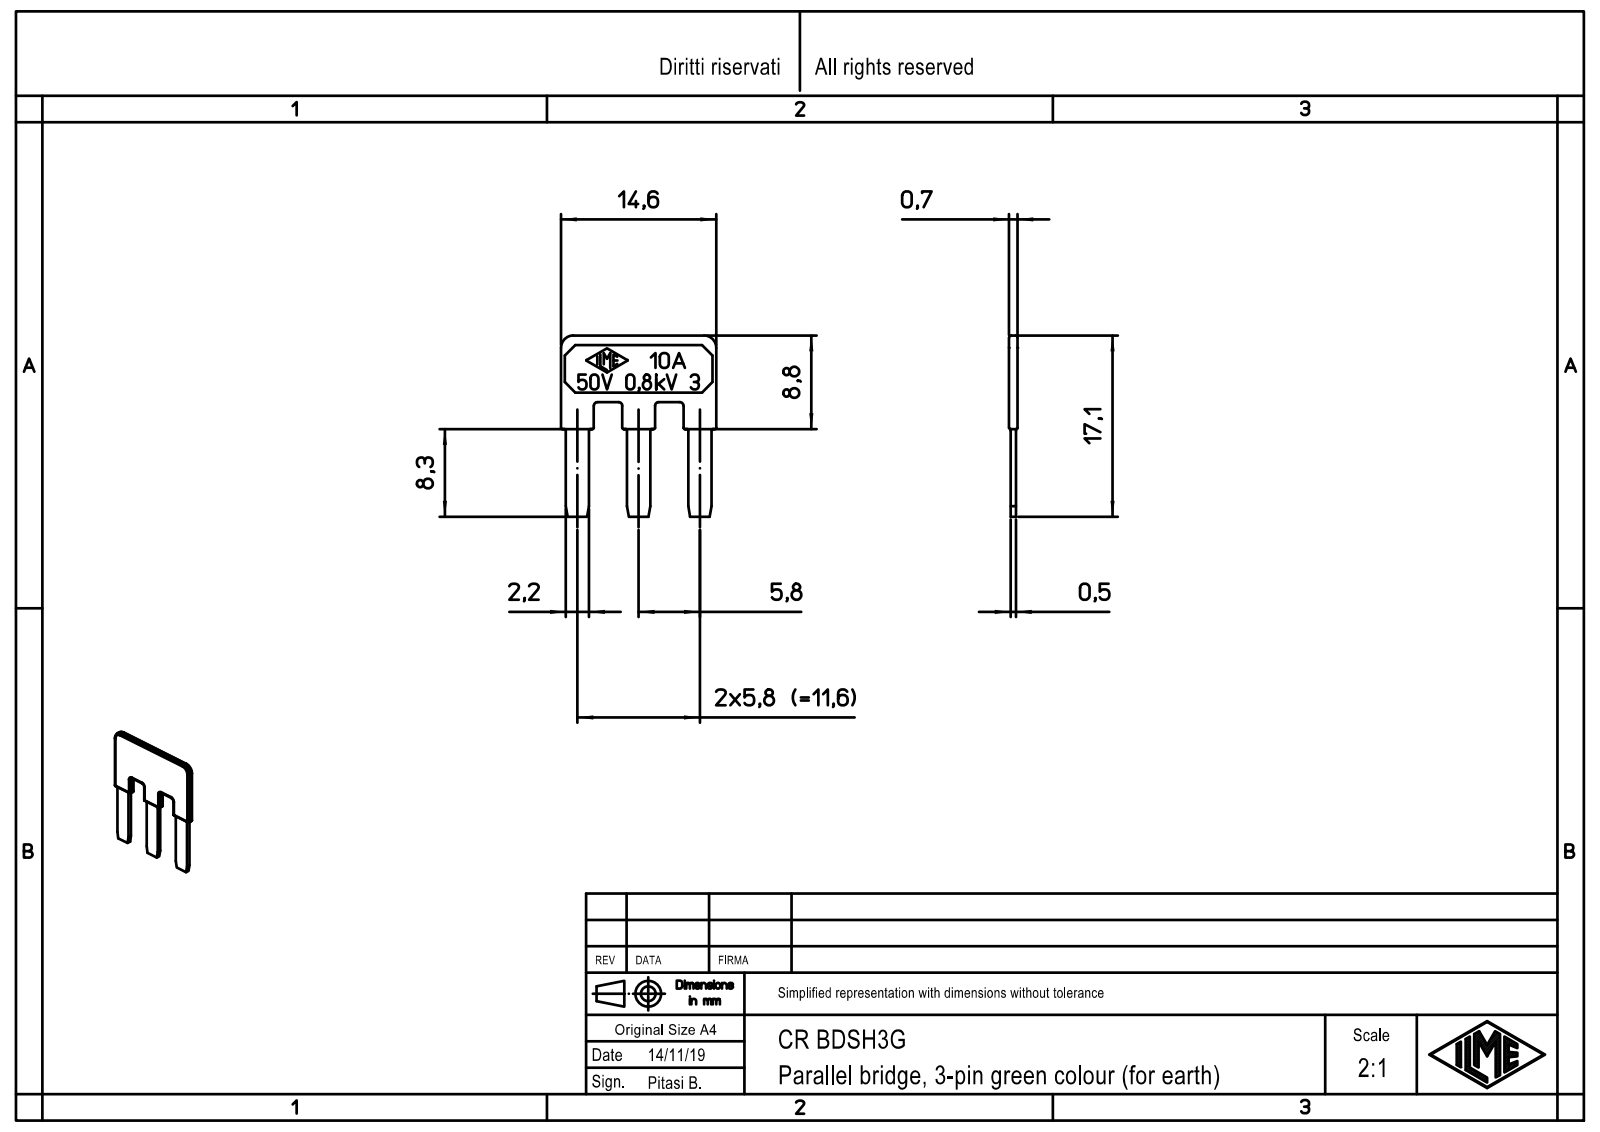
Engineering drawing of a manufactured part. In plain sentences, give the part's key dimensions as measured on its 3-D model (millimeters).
The part is named "PONTE_03G". Its 3-D file was written by "Creo Elements/Direct Modeling 20.1B 02-Apr-2019 (C) Parametric Technology GmbH (AUTOMOTIVE_DESIGN)". It is 1 solid with 107 faces: 41 planar, 42 cylindrical and 24 other. Overall it measures 17.15 by 14.7 by 0.8 millimeters. Its volume is 119 cubic millimeters and its surface area 400 square millimeters. Partial cylindrical surfaces (rounded edges, fillets, slot ends): 16 of radius 0.2, 8 of radius 0.1, 6 of radius 0.15, 4 of radius 0.35, 2 of radius 1.15. The main face-to-face distances are 0.65, 0.8, 0.5, 5.8, 2.2, 0.45, 2.65, 11.6, 6.25, 8.45.
